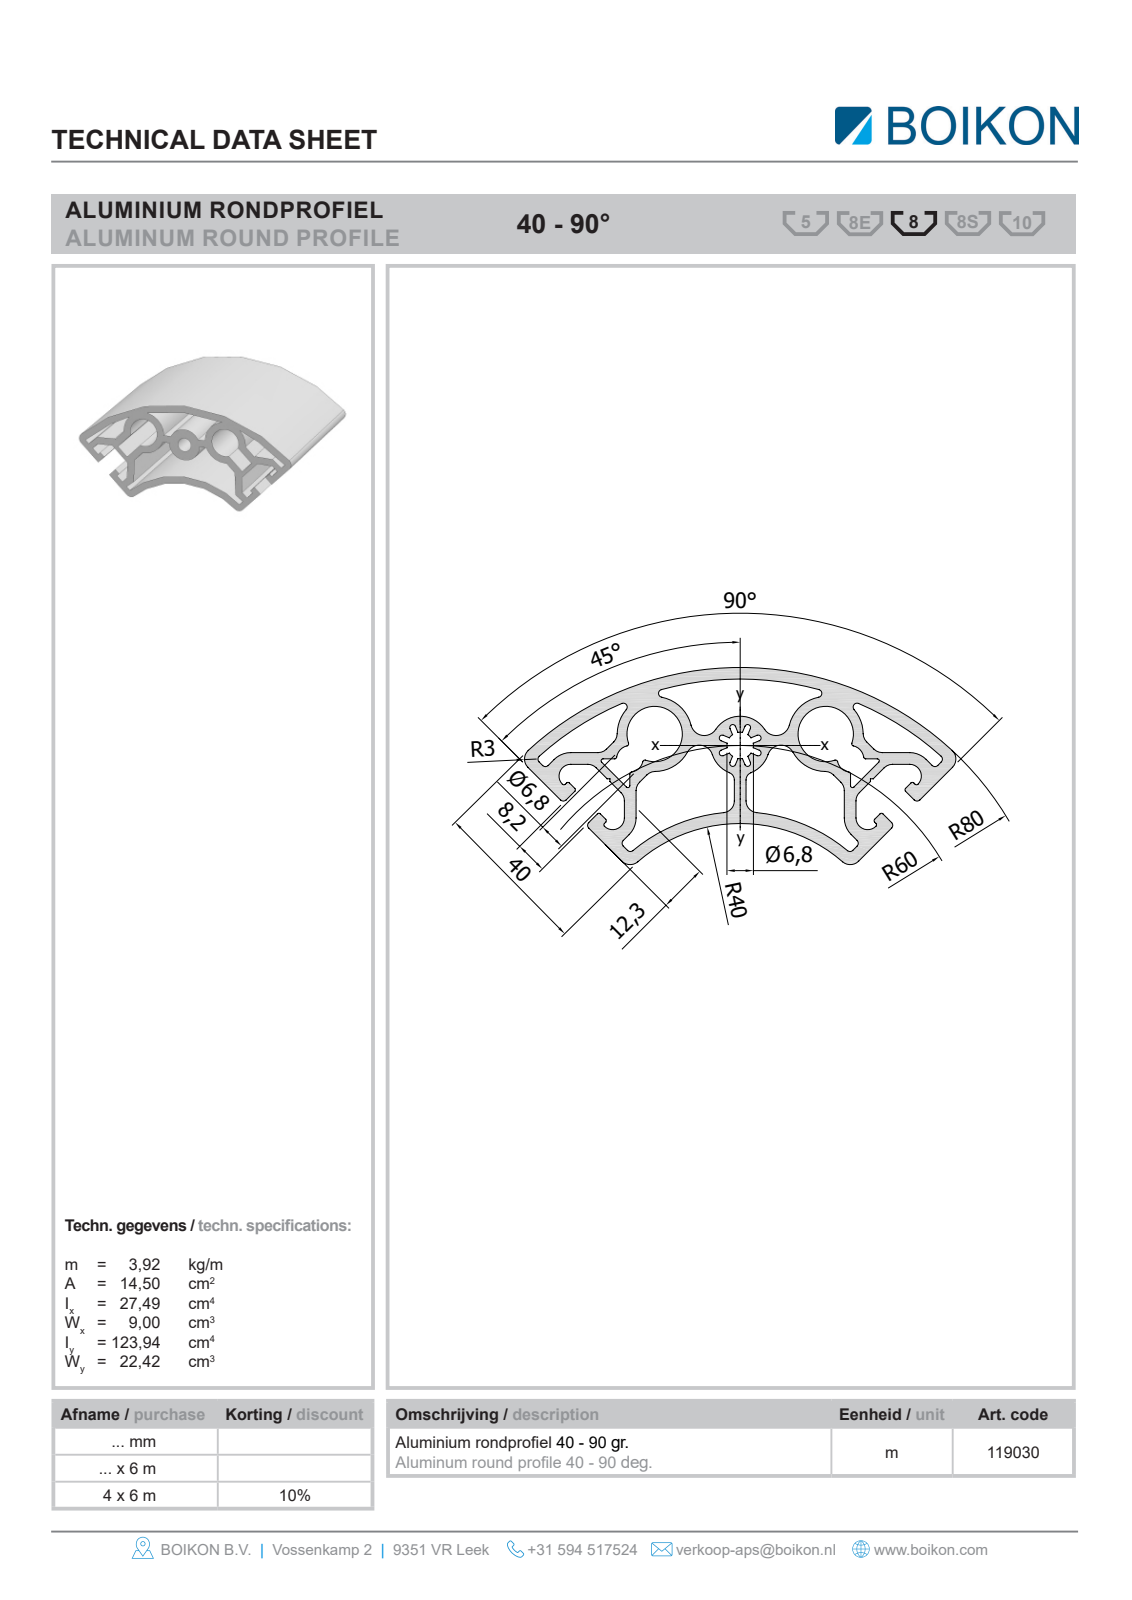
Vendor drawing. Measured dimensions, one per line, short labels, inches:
name: Root; 119030Rondprofiel 40-90gr.BOIKON0
written by: HiCAD 2013 1802.4 Build 509 (AUTOMOTIVE_DESIGN)
unit: in
bodies: 1 solid, 81 faces (56 planar, 25 cylindrical, 0 other)
size: 39.37 × 3.147 × 3.147
volume: 100.2 in³; area: 1 402 in²
holes: 2× ⌀0.551, 1× ⌀0.268
bosses: 1× ⌀0.622
rounds: 4× R0.118, 2× R0.413, 1× R1.575, 1× R1.713, 1× R1.811, 1× R2.913, 1× R3.012, 1× R3.15
face distances: 0.138, 0.114, 1.752, 0.299, 0.406, 0.476, 0.362, 2.02, 2.496, 2.382
hole spacings: 0.847, 0.848, 1.67
